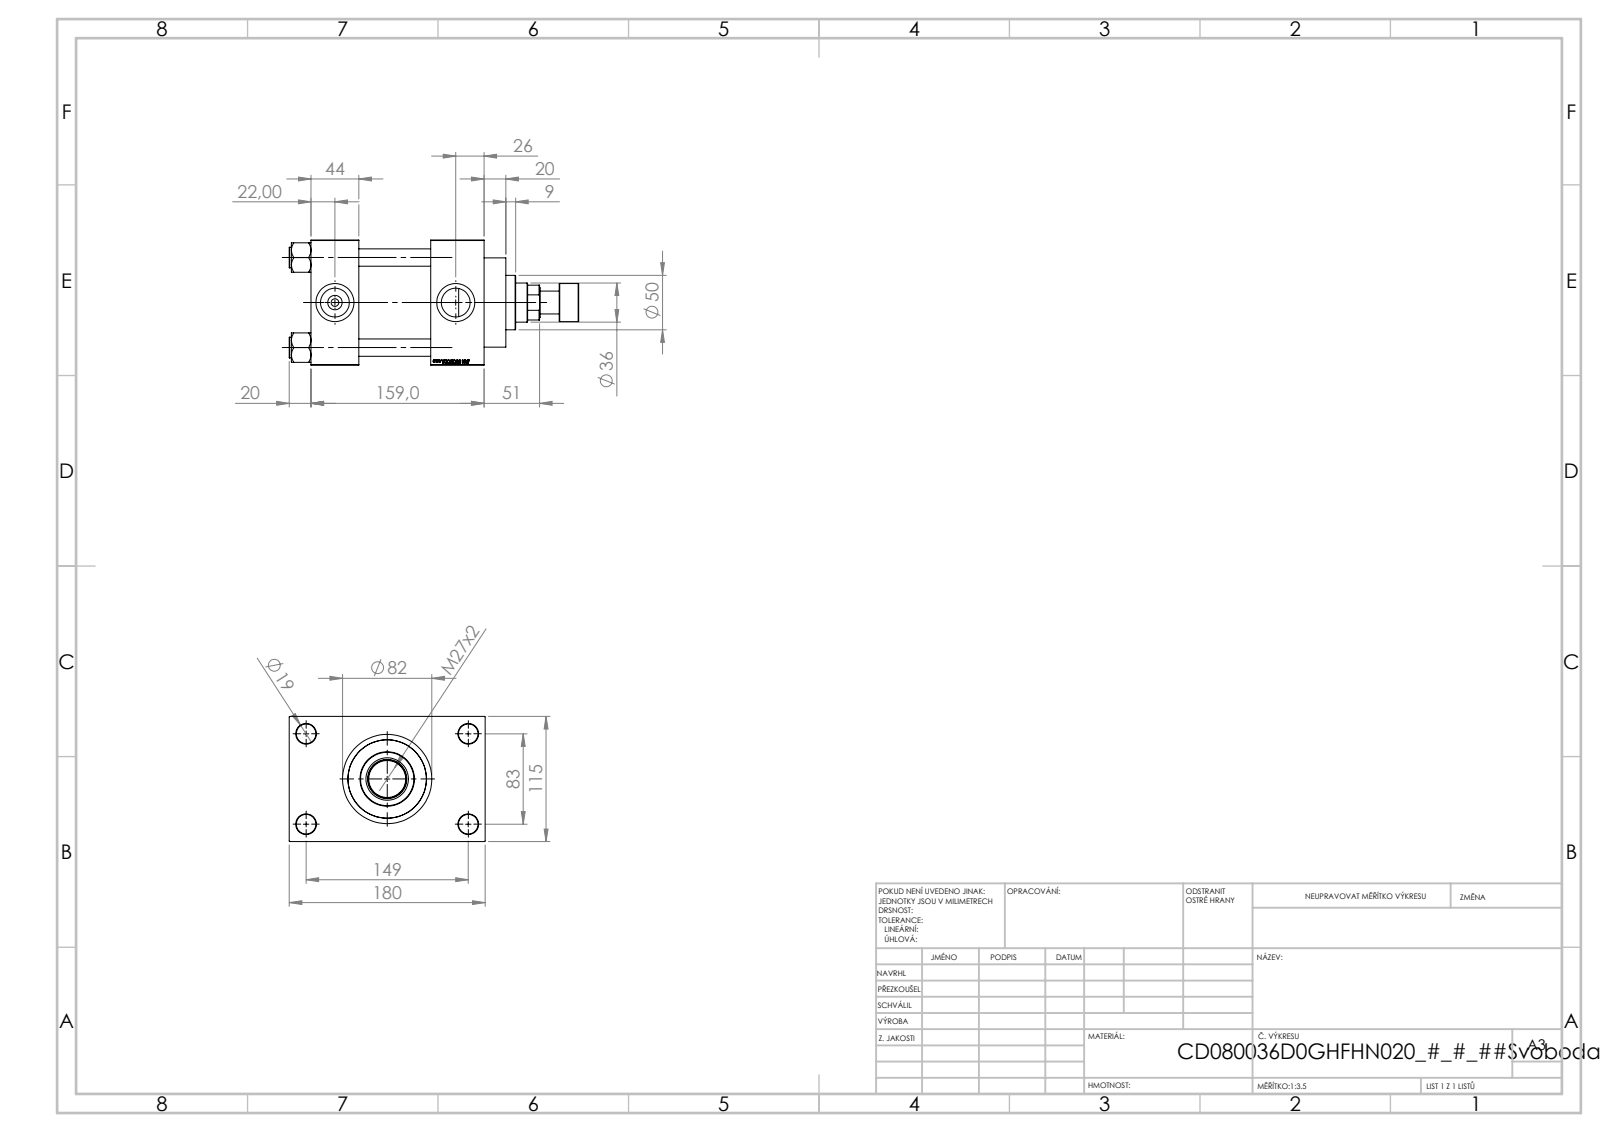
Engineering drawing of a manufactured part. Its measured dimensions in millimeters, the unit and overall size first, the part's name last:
Units: millimetres
Overall size (bounding box): 266 × 180 × 115
Round holes (diameter × count): ⌀16 ×4, ⌀18 ×4, ⌀7 ×2, ⌀26.44 ×2, ⌀35 ×2, ⌀25.5 ×1, ⌀36 ×1, ⌀39 ×1, ⌀61 ×1, ⌀72 ×1, ⌀80 ×1
Round bosses / shafts (diameter × count): ⌀19 ×4, ⌀86 ×1, ⌀82 ×1, ⌀50 ×1, ⌀35 ×1, ⌀21 ×1
Main face-to-face distances: 115, 66, 49, 110, 44, 159, 32.5, 147.5, 20, 69
Hole centre spacings: 33.15, 58.48, 82.7, 85.28, 89.24, 115.85, 142.43, 83
Volume: 2 003 000 mm³ · Surface area: 302 161 mm²
Bodies: 12 solids, 1165 faces (549 planar, 92 cylindrical, 524 other)
Part name (STEP PRODUCT): V215CR_ROD_END_F; V215CD_D_Body; V215CD_NUT_M5_D; V215CD_D_TYCINKA (+2 more)
STEP written by: SolidWorks 2019 (CONFIG_CONTROL_DESIGN)
